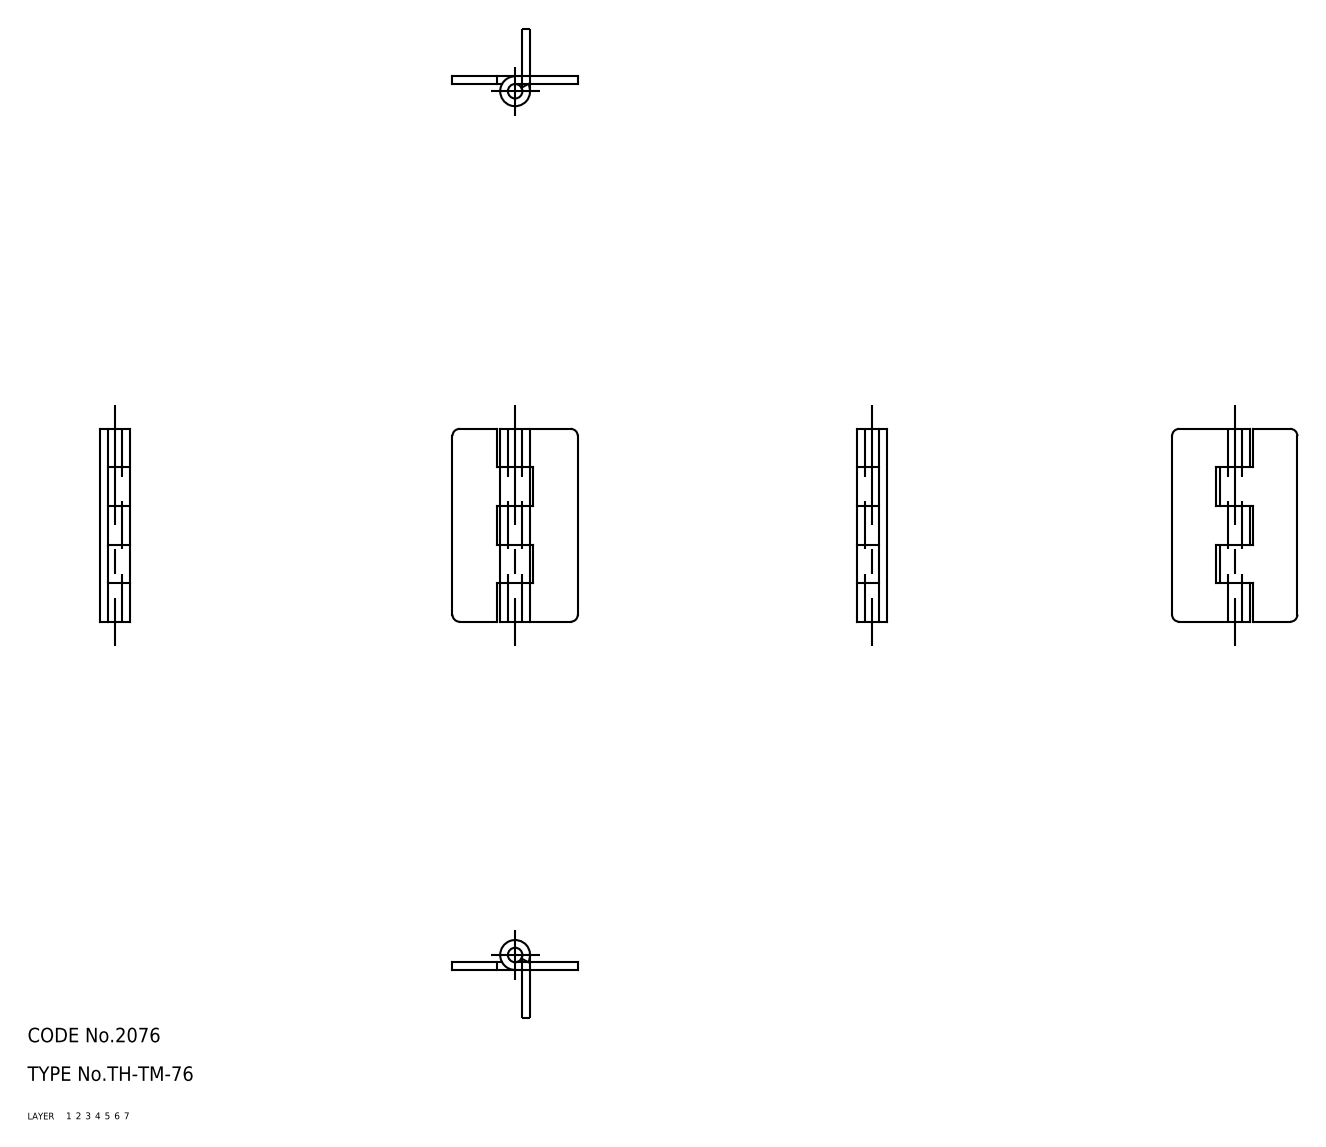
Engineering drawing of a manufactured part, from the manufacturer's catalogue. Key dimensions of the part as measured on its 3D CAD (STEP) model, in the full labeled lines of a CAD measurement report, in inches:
Part name (STEP PRODUCT): hinge piece_B; hinge piece_A; shaft; TH_TM_76_25465_36
STEP written by: CADfix (AUTOMOTIVE_DESIGN)
Units: inches
Bodies: 3 solids, 46 faces (0 planar, 0 cylindrical, 46 other)
Overall size (bounding box): 1.575 × 1.024 × 0.244
Volume: 0.15 in³ · Surface area: 5.709 in²
